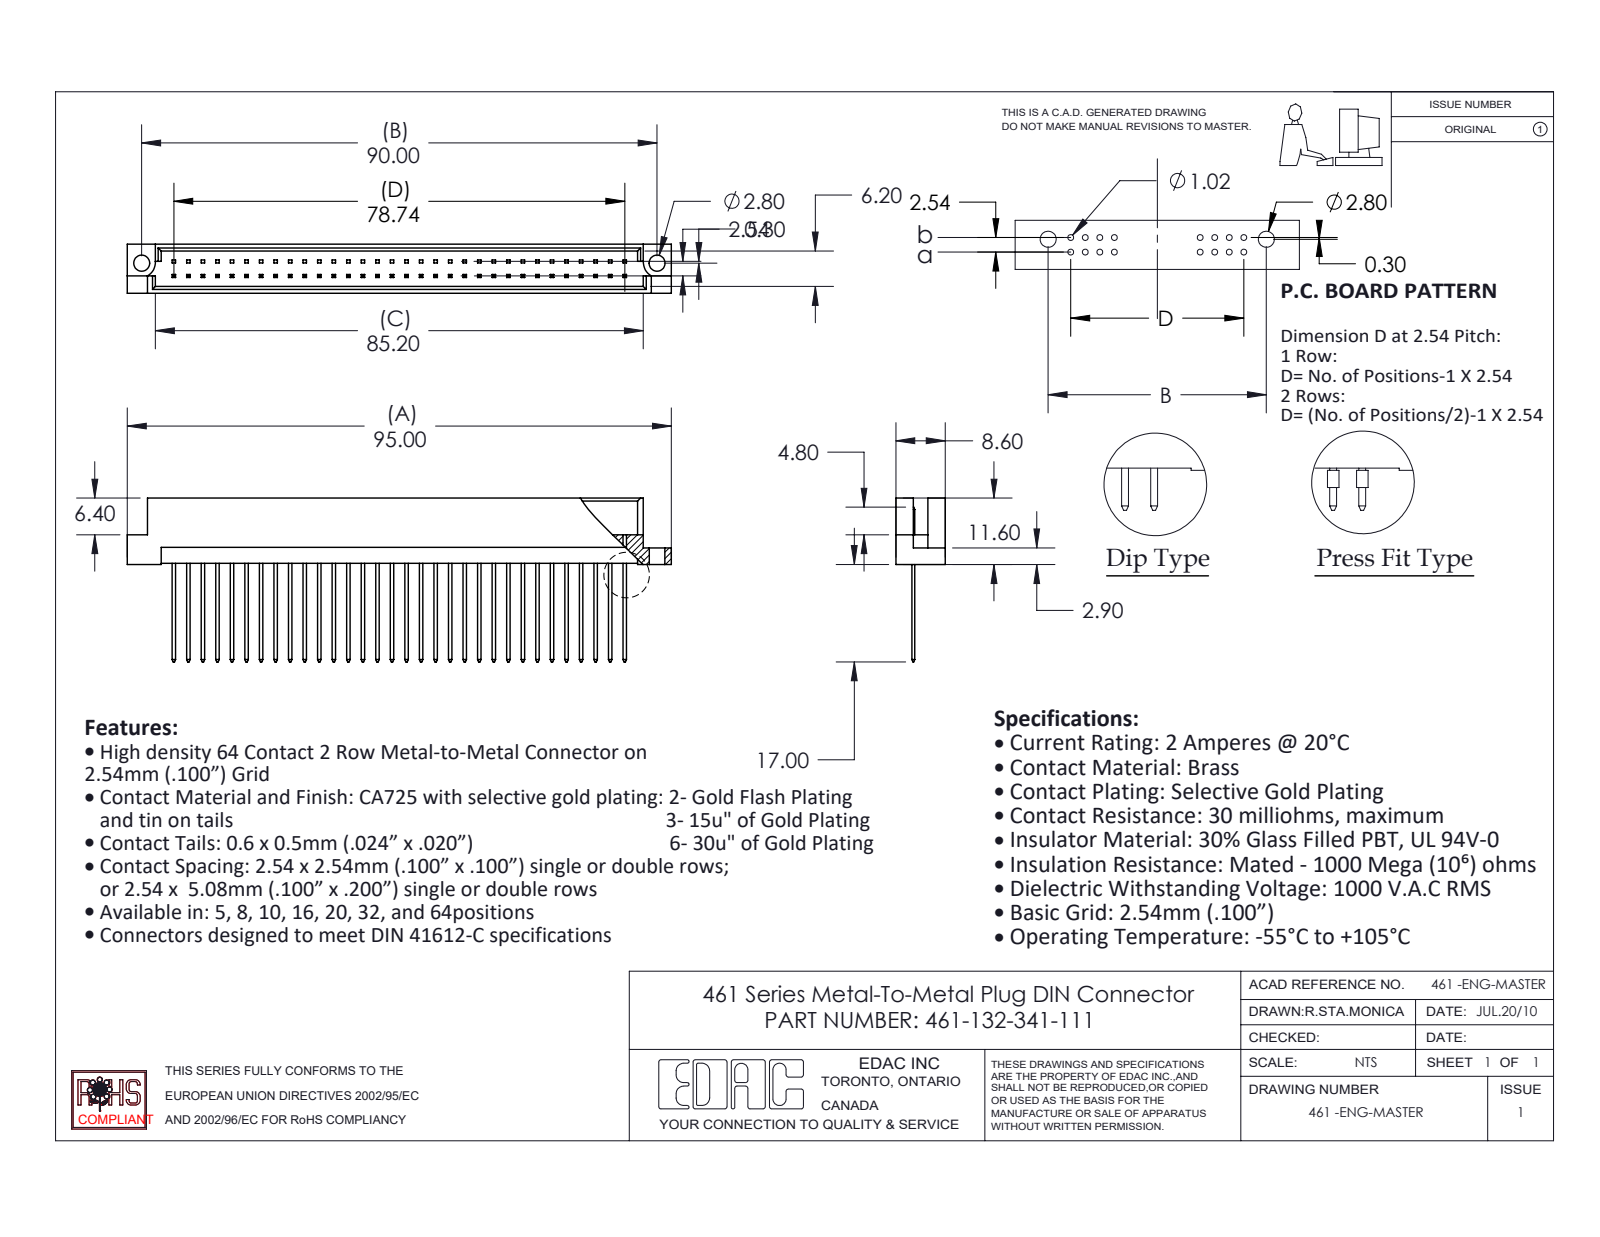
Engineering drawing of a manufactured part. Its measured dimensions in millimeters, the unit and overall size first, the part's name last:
Units: millimetres
Overall size (bounding box): 95 × 28.6 × 8.6
Round holes (diameter × count): ⌀2.8 ×2
Partial cylindrical surfaces — rounded edges, fillets, slot ends (radius × count): R2.8 ×2
Main face-to-face distances: 1.2, 7.4, 8.6, 6.2, 3.28, 5.32, 2.08, 4.12, 2.78, 5.82
Hole centre spacings: 90
Volume: 4 912 mm³ · Surface area: 7 560 mm²
Bodies: 33 solids, 753 faces (746 planar, 7 cylindrical, 0 other)
Part name (STEP PRODUCT): 461-132-341-111; 461-290_41; 461 Part_64
STEP written by: SolidWorks 2020 (CONFIG_CONTROL_DESIGN)
